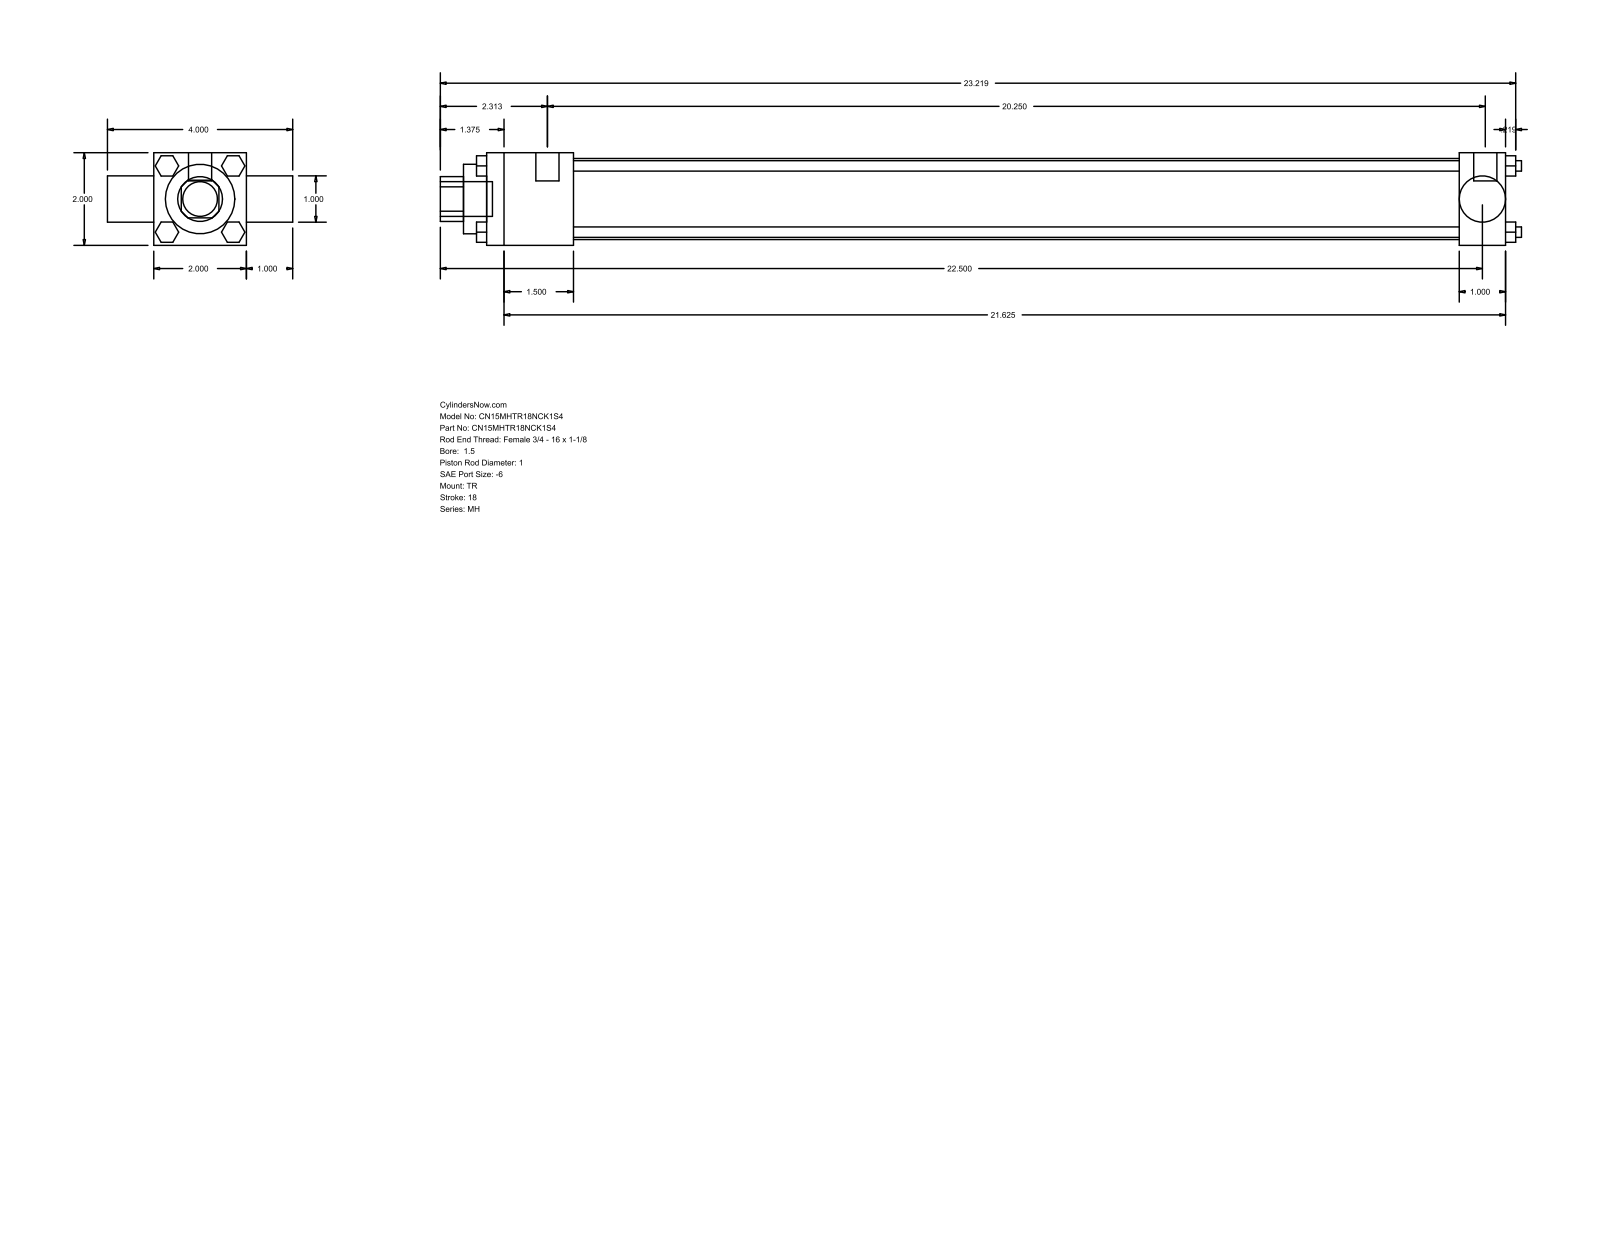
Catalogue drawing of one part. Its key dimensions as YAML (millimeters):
part_name: "MH_TR__0150_1"
step_written_by: "GSSL Pune (CONFIG_CONTROL_DESIGN)"
units: millimeters
bodies: {solids: 0, faces: 120, planar: 92, cylindrical: 28, other: 0}
overall_size: [592.93, 101.6, 50.8]
round_holes:
  - {diameter: 25.35, count: 1}
  - {diameter: 25.4, count: 1}
  - {diameter: 38.1, count: 1}
  - {diameter: 44.45, count: 1}
round_bosses_or_shafts:
  - {diameter: 5.71, count: 4}
  - {diameter: 5.56, count: 3}
  - {diameter: 12.7, count: 2}
  - {diameter: 19.05, count: 1}
partial_cylinders:
  - {radius: 12.29, count: 1}
face_to_face_distances: [50.8, 25.4, 558.8, 76.2, 47.63, 511.17, 533.4, 485.77, 564.36, 12.7]
